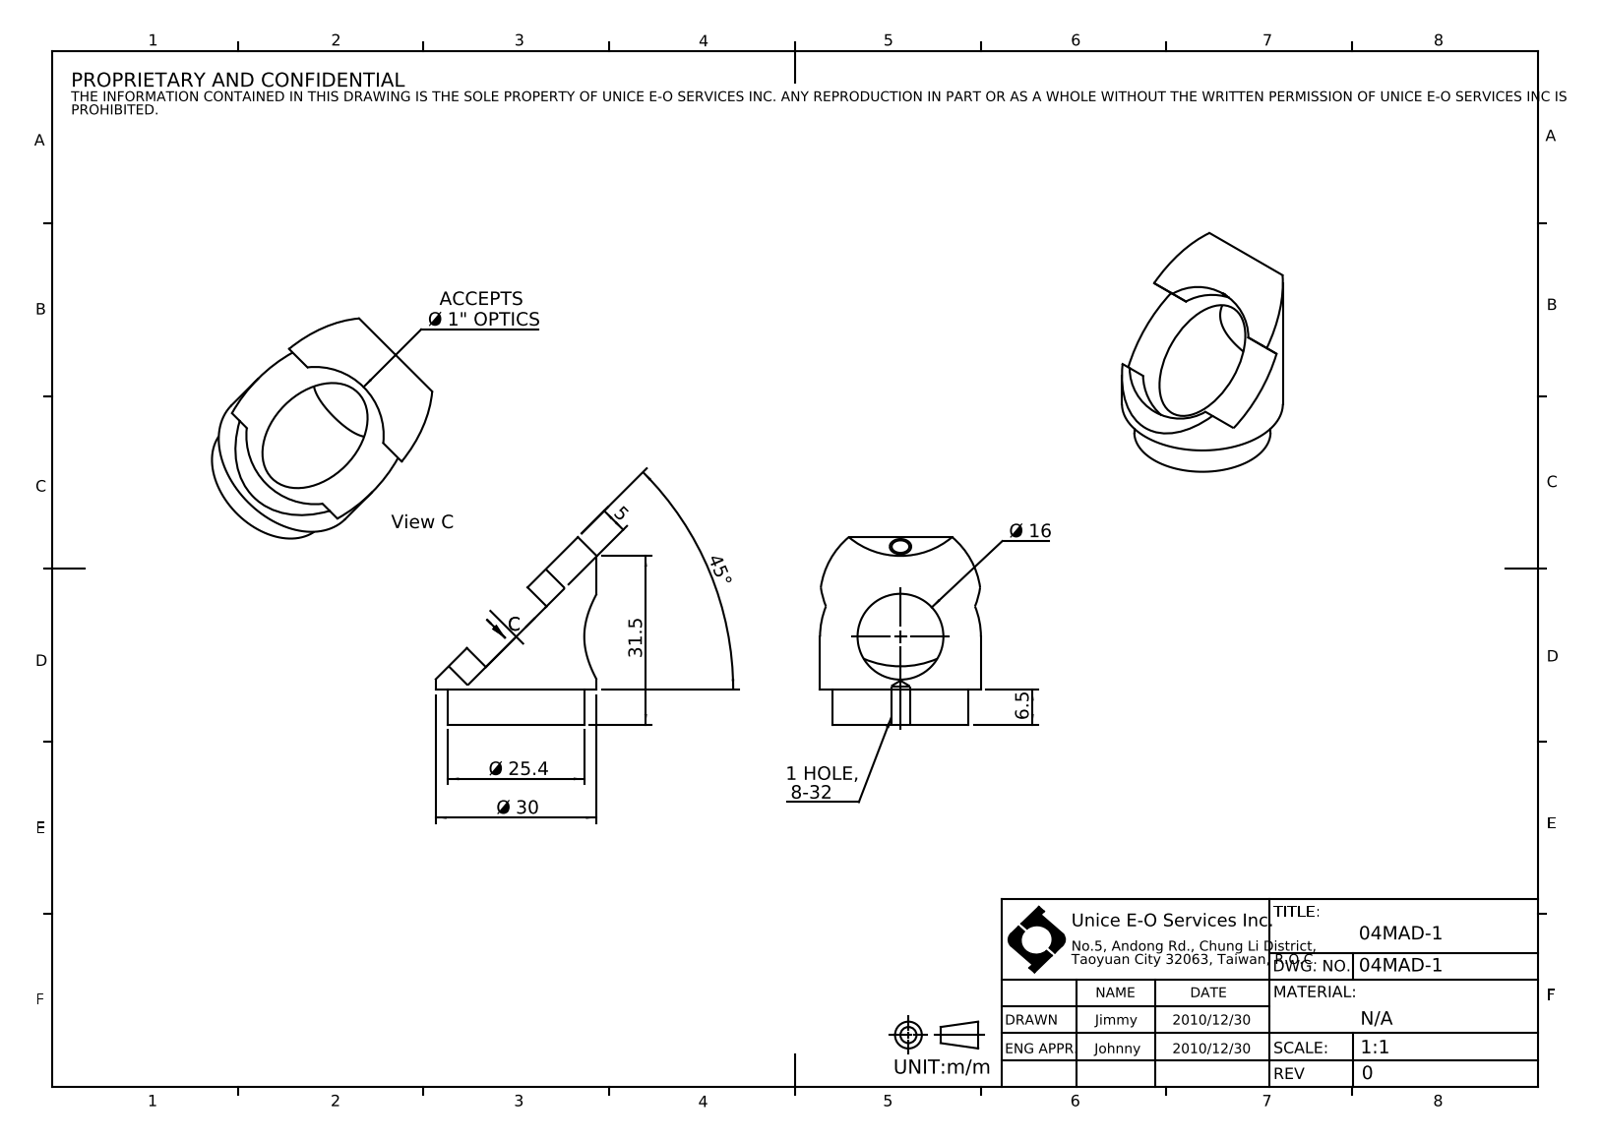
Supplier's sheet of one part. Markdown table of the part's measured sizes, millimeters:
| quantity | value |
| --- | --- |
| part name | 04MAD-1 |
| STEP written by | SolidWorks 2016 (CONFIG_CONTROL_DESIGN) |
| units | millimeters |
| bodies | 1 solid, 25 faces (10 planar, 13 cylindrical, 2 other) |
| overall size | 35 × 30 × 30 |
| volume | 9 146 mm³ |
| surface area | 4 238 mm² |
| round holes (diameter × count) | 3.3 × 1, 3.45 × 1, 16 × 1 |
| round bosses / shafts (diameter × count) | 30 × 1, 25.4 × 1 |
| partial cylindrical surfaces (radius × count) | 12.8 × 1 |
| main face-to-face distances | 5, 6.5, 13.26, 16, 29.26 |
